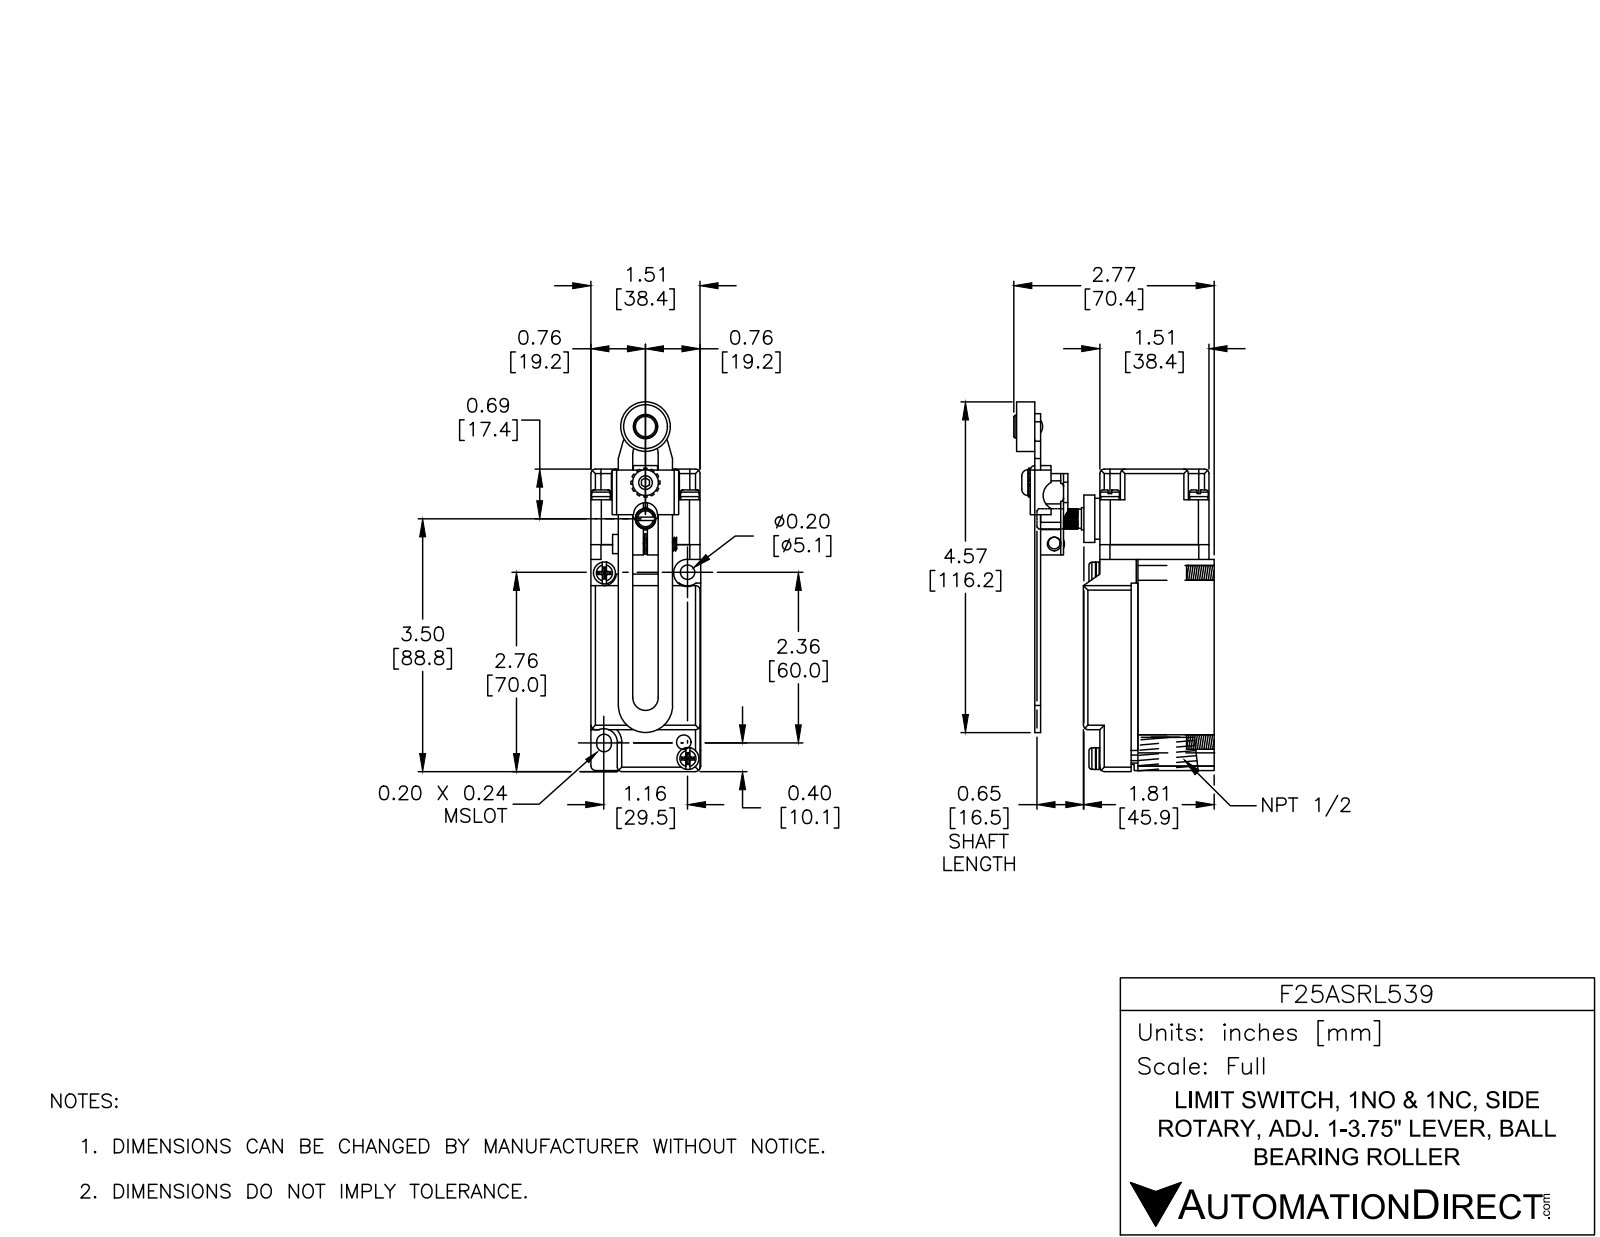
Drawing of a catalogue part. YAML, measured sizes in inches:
part_name: "F25ASRL539; Imported130; Imported129; Imported134 (+8 more)"
step_written_by: "SolidWorks 2002296 (CONFIG_CONTROL_DESIGN)"
units: inches
bodies: {solids: 21, faces: 1108, planar: 537, cylindrical: 259, other: 312}
overall_size: [6.526, 2.771, 1.52]
volume: 10.57
surface_area: 80.5
round_holes:
  - {diameter: 0.177, count: 4}
  - {diameter: 0.2, count: 4}
  - {diameter: 0.19, count: 3}
  - {diameter: 0.203, count: 2}
  - {diameter: 0.11, count: 1}
  - {diameter: 0.156, count: 1}
  - {diameter: 0.202, count: 1}
  - {diameter: 0.209, count: 1}
  - {diameter: 0.249, count: 1}
  - {diameter: 0.283, count: 1}
  - {diameter: 0.58, count: 1}
  - {diameter: 0.605, count: 1}
round_bosses_or_shafts:
  - {diameter: 0.26, count: 4}
  - {diameter: 0.25, count: 4}
  - {diameter: 0.302, count: 2}
  - {diameter: 0.3, count: 2}
  - {diameter: 0.687, count: 1}
  - {diameter: 0.655, count: 1}
  - {diameter: 0.565, count: 1}
  - {diameter: 0.358, count: 1}
partial_cylinders:
  - {radius: 0.062, count: 32}
  - {radius: 0.03, count: 16}
  - {radius: 0.015, count: 8}
  - {radius: 0.145, count: 8}
  - {radius: 0.14, count: 4}
  - {radius: 0.04, count: 2}
  - {radius: 0.1, count: 2}
  - {radius: 0.102, count: 2}
face_to_face_distances: [0.094, 1.149, 1.055, 1.52, 0.66, 0.754, 1.809, 1.51, 0.674, 1.333]
hole_center_spacings: [1.23, 1.23, 1.74, 2.815, 0.225, 0.23, 0.235, 0.27]
